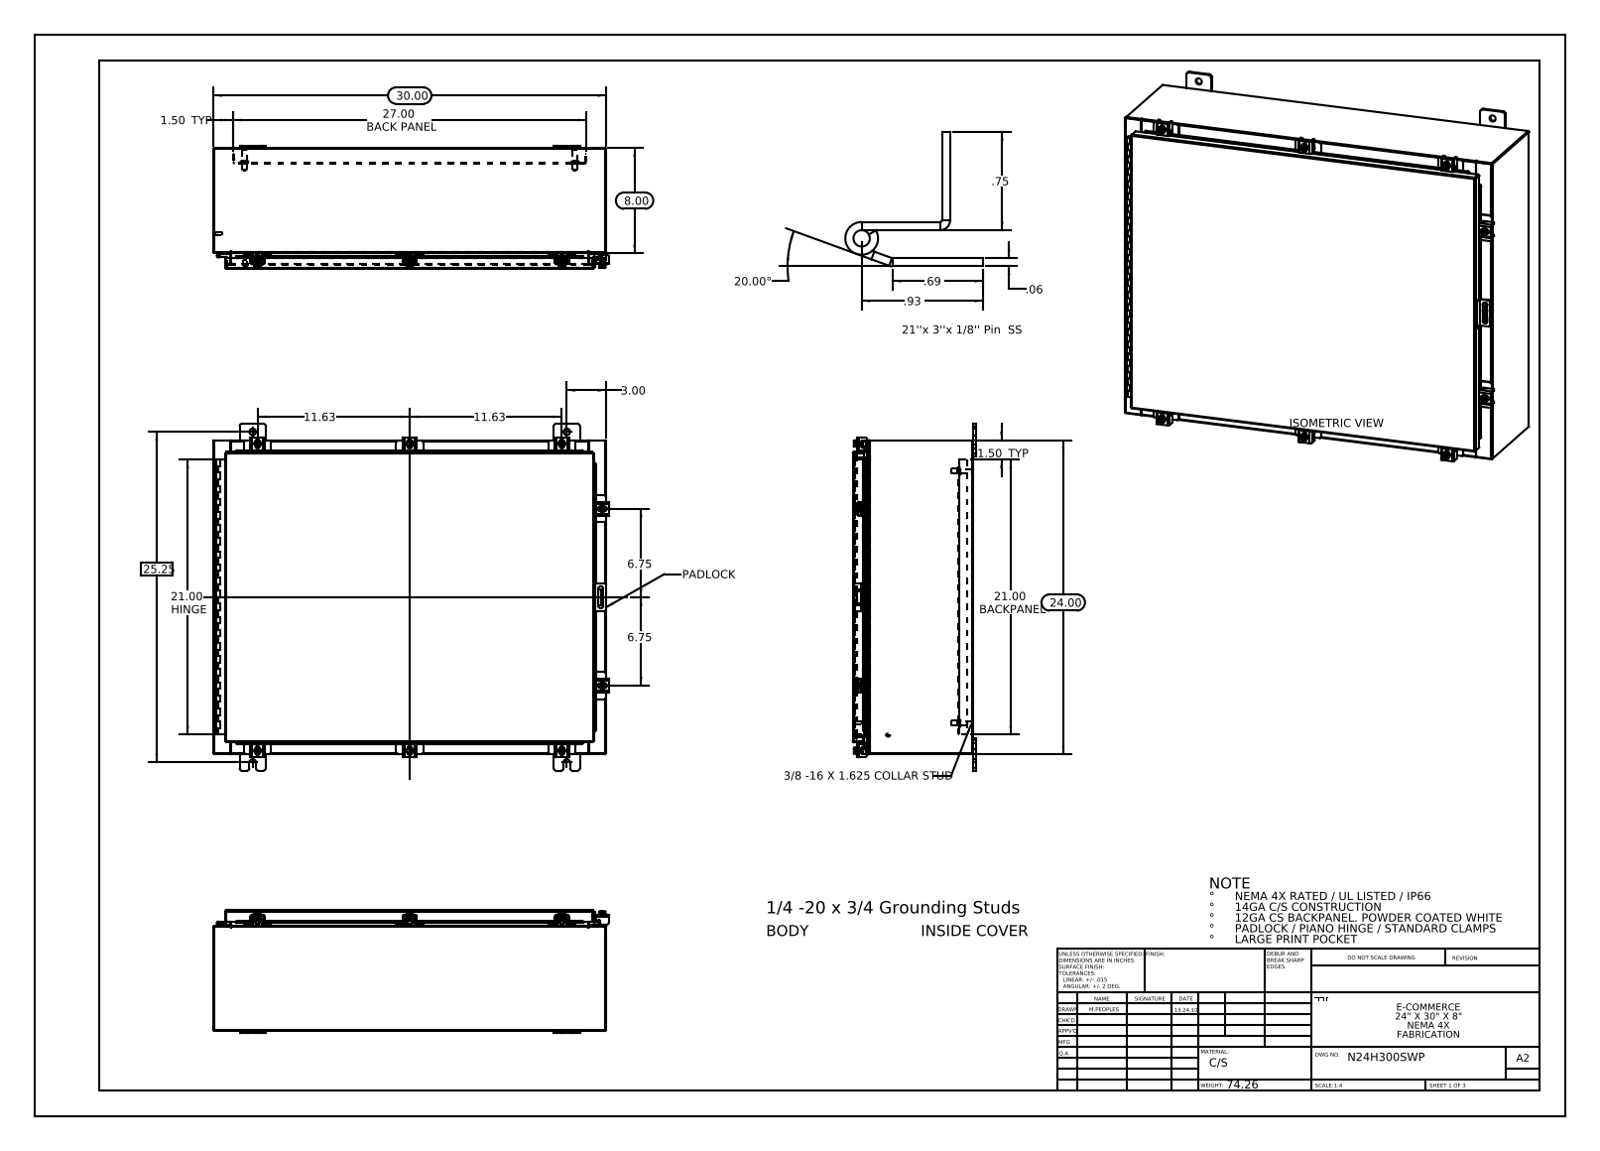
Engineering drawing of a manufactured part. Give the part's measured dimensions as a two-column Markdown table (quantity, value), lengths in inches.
| quantity | value |
| --- | --- |
| part name | N24H3008SSWP Clamp Bracket; N24H3008SSWP Hinge Cover Side; N24H3008SSWP 22101002; N24H3008SSWP Clamp Top (+8 more) |
| STEP written by | SolidWorks 2013 (CONFIG_CONTROL_DESIGN) |
| units | inches |
| bodies | 59 solids, 1969 faces (1034 planar, 811 cylindrical, 124 other) |
| overall size | 30.211 × 26.5 × 9.389 |
| volume | 261 in³ |
| surface area | 6 535 in² |
| round holes (diameter × count) | 0.213 × 8, 0.26 × 8, 0.5 × 8, 0.125 × 2 |
| round bosses / shafts (diameter × count) | 0.25 × 9, 0.5 × 8, 0.399 × 8, 0.625 × 4, 0.375 × 4, 0.33 × 4, 0.315 × 2, 0.236 × 2 |
| partial cylindrical surfaces (radius × count) | 0.06 × 38, 0.013 × 25, 0.19 × 24, 0.088 × 21, 0.12 × 16, 0.141 × 16, 0.05 × 11, 0.08 × 10 |
| main face-to-face distances | 0.075, 9.126, 9.051, 9.201, 0.104, 1, 1.075, 8.051, 8.126, 1.179 |
| hole center spacings | 21.374, 24, 26.174, 23.451, 1.858, 2.326, 2.326, 3.065 |
